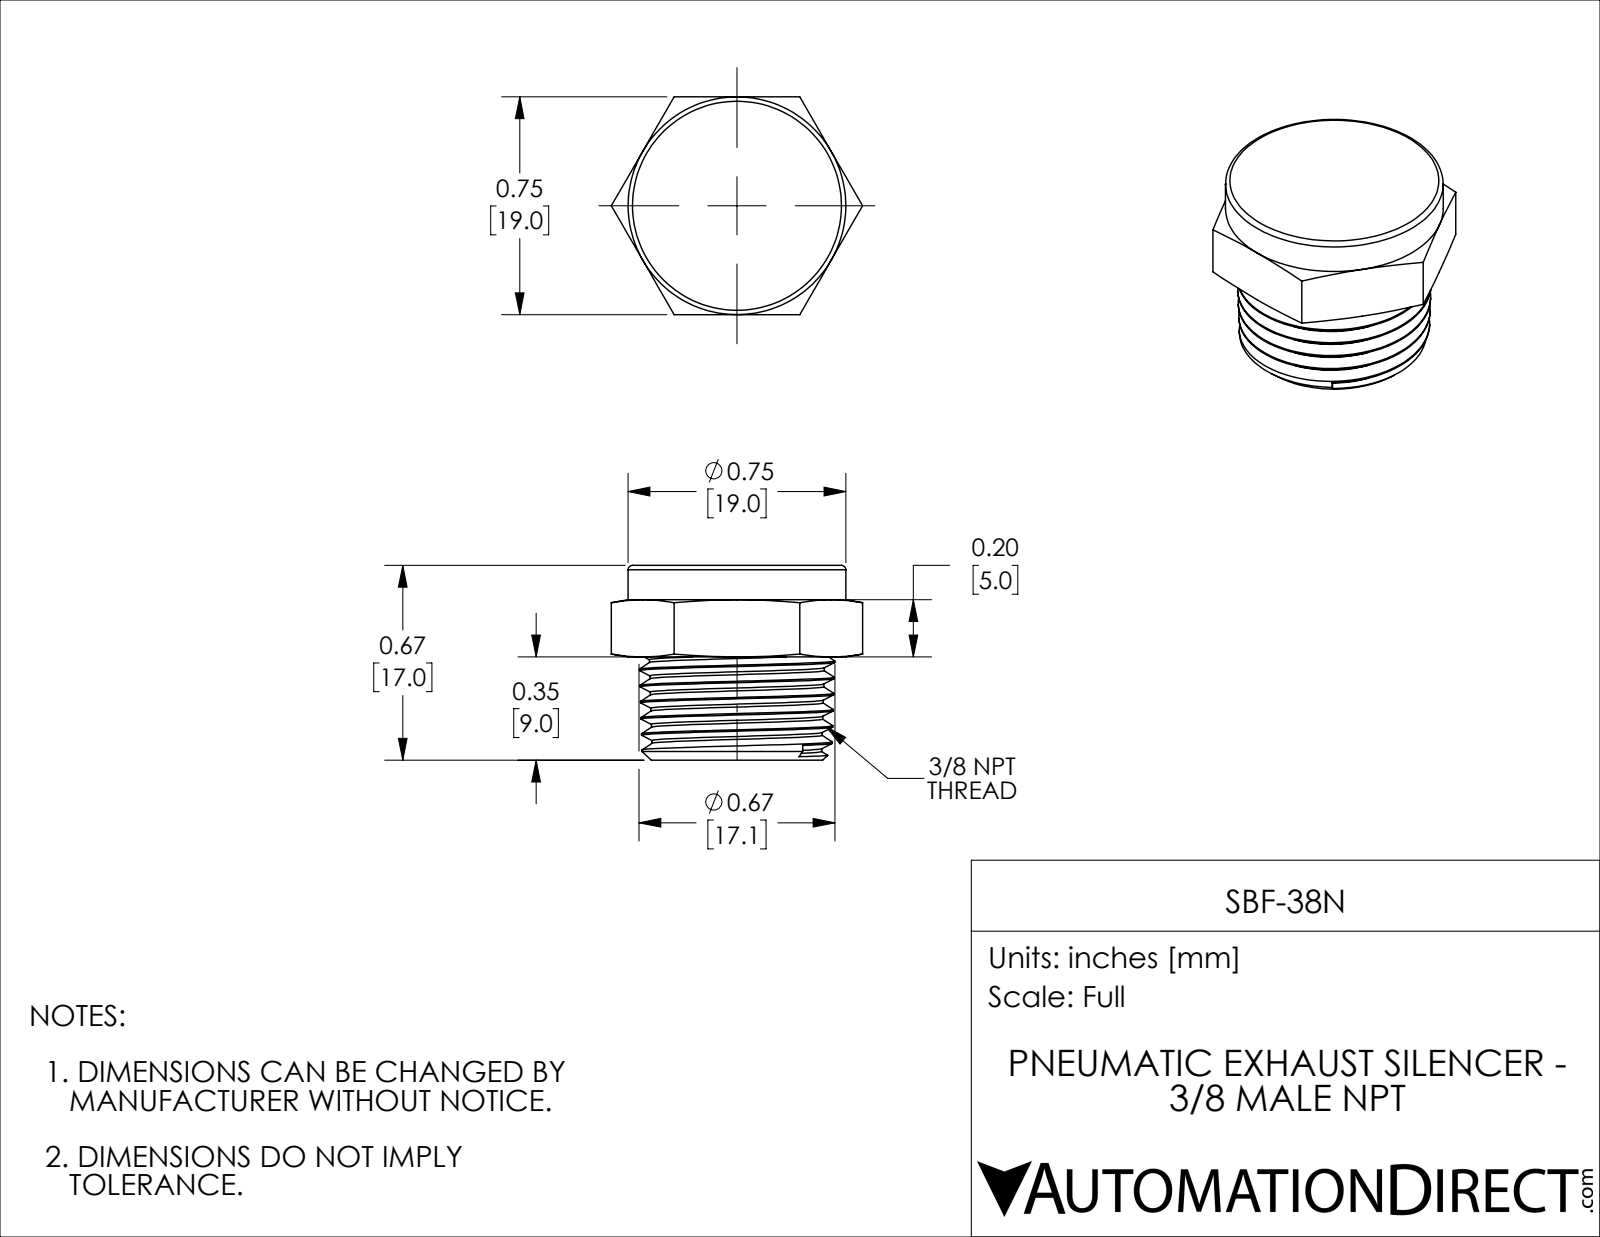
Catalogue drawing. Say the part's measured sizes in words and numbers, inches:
The part is named "SBF-38N". Its 3-D file was written by "SolidWorks 2021 (CONFIG_CONTROL_DESIGN)". It is 1 solid with 47 faces: 11 planar, 4 cylindrical and 32 other. Overall it measures 0.864 by 0.748 by 0.669 inches. Its volume is 0.217 cubic inches and its surface area 3.357 square inches. Round holes: 1 of diameter 0.314. Round bosses or shafts: 1 of diameter 0.748. The main face-to-face distances are 0.748, 0.669, 0.354, 0.315, 0.5, 0.146, 0.169.
